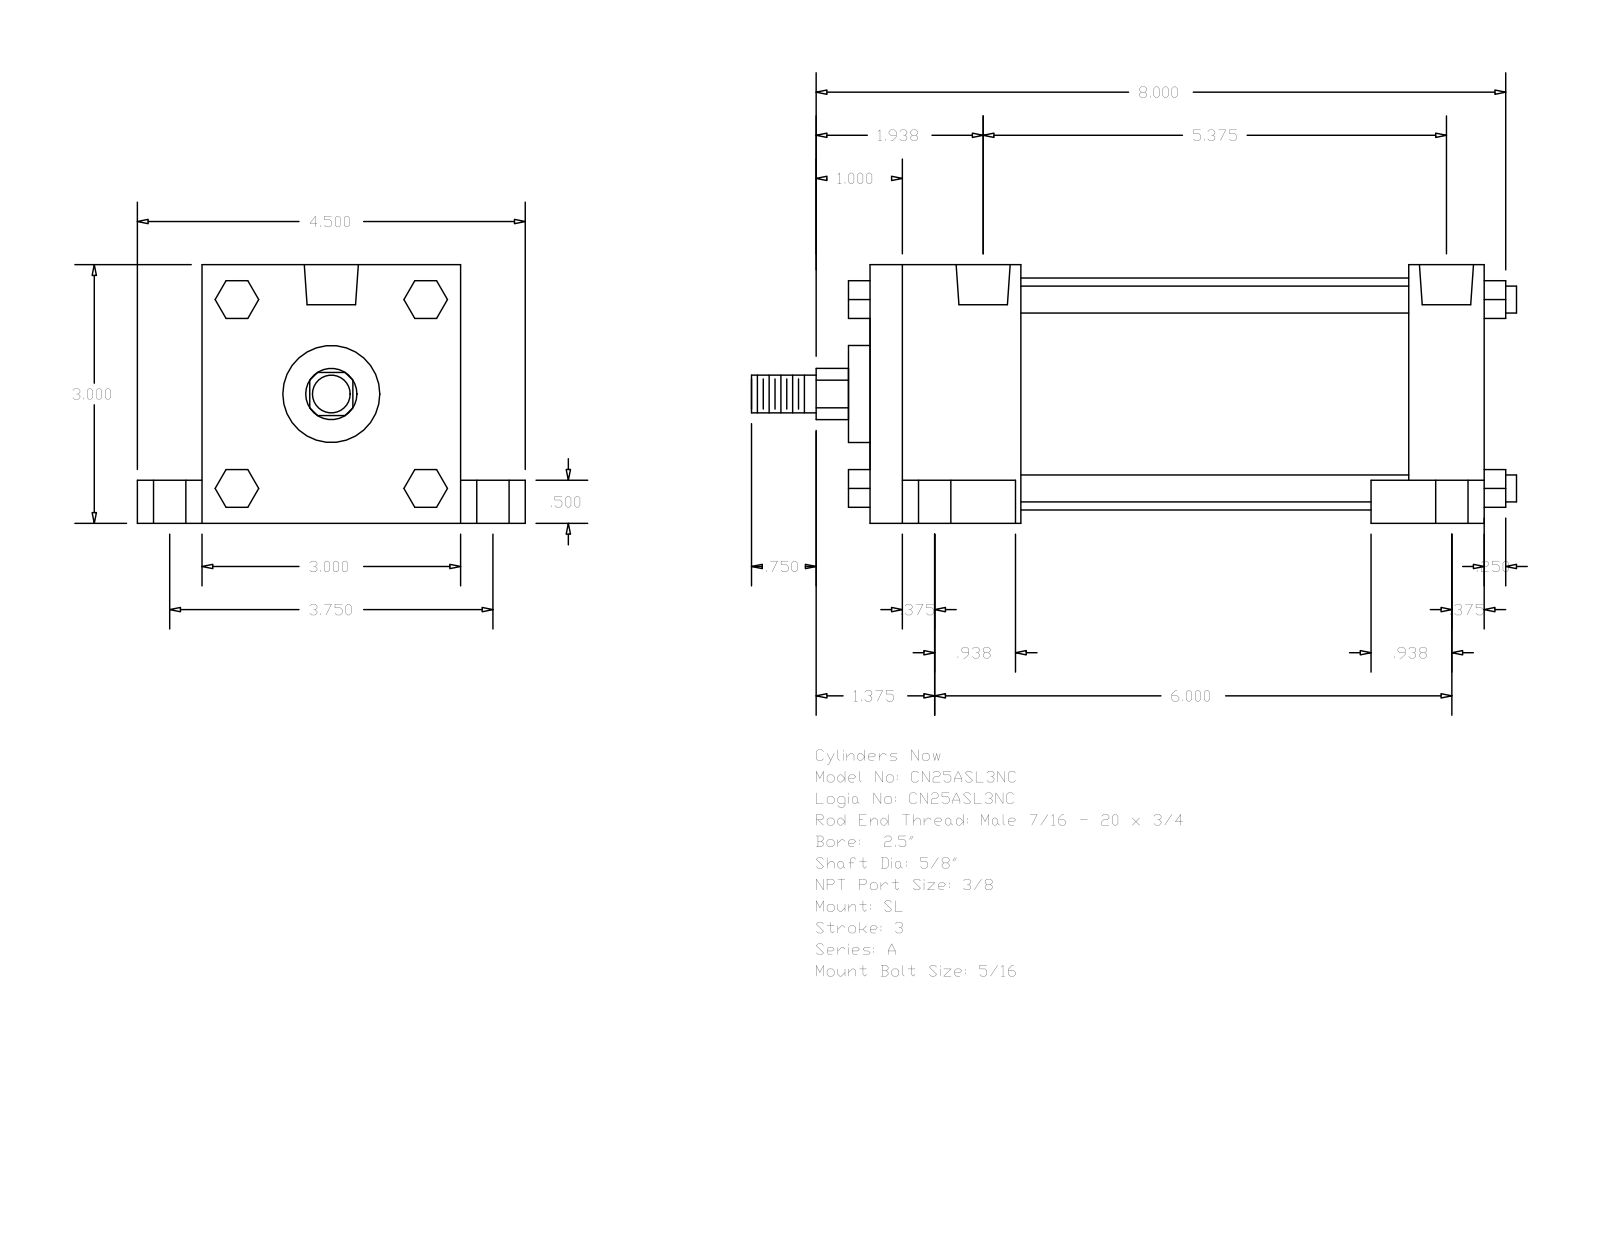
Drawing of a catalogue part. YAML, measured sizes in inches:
part_name: "A_SL__0250_0.625"
step_written_by: "GSSL Pune (CONFIG_CONTROL_DESIGN)"
units: inches
bodies: {solids: 0, faces: 148, planar: 112, cylindrical: 36, other: 0}
overall_size: [8.875, 4.5, 3]
round_holes:
  - {diameter: 0.219, count: 4}
  - {diameter: 0.375, count: 4}
  - {diameter: 0.625, count: 4}
  - {diameter: 0.627, count: 2}
round_bosses_or_shafts:
  - {diameter: 0.313, count: 4}
  - {diameter: 2.69, count: 1}
  - {diameter: 1.125, count: 1}
  - {diameter: 0.625, count: 1}
  - {diameter: 0.437, count: 1}
partial_cylinders:
  - {radius: 0.297, count: 1}
face_to_face_distances: [3, 7.125, 1.75, 5.375, 6.25, 4.5, 0.875, 2.5, 0.5, 0.75]
hole_center_spacings: [0.094, 1.875, 1.876, 1.933, 1.957, 3.75, 5.469, 5.563]
